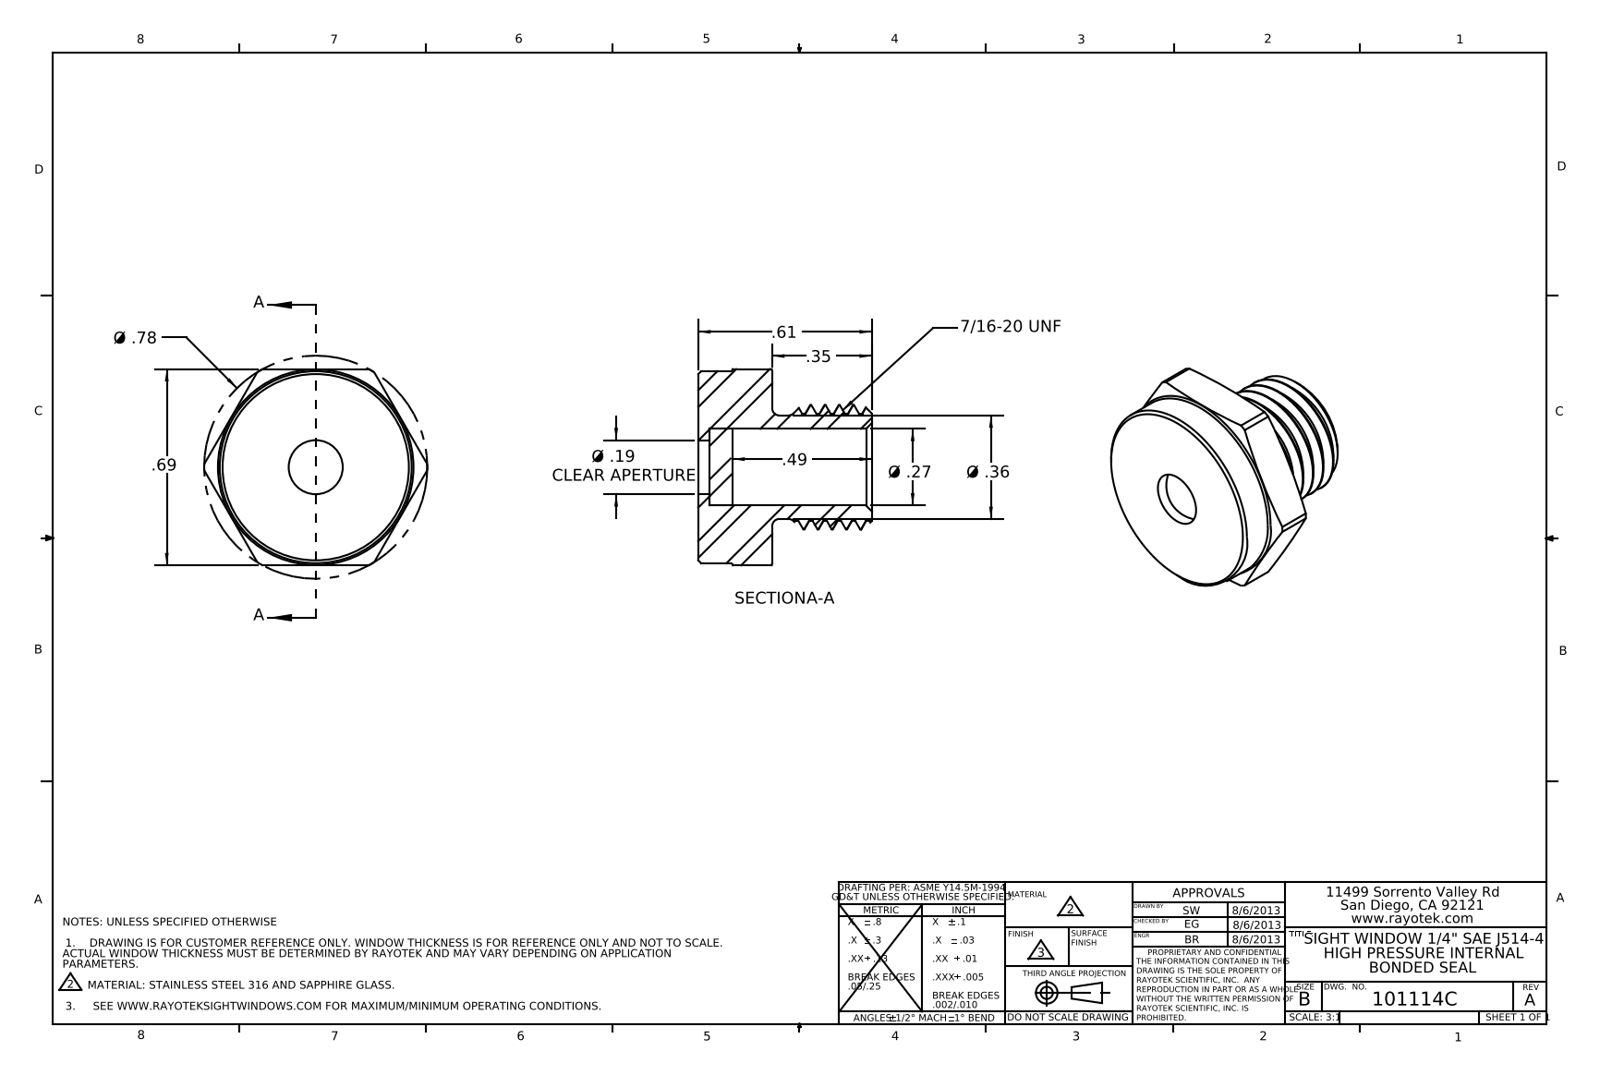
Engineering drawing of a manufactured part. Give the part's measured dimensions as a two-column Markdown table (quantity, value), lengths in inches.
| quantity | value |
| --- | --- |
| part name | 403114 |
| STEP written by | SolidWorks 2012 (AUTOMOTIVE_DESIGN) |
| units | inches |
| bodies | 2 solids, 61 faces (12 planar, 26 cylindrical, 23 other) |
| overall size | 0.785 × 0.69 × 0.61 |
| volume | 0.113 in³ |
| surface area | 2.652 in² |
| round holes (diameter × count) | 0.19 × 1, 0.27 × 1 |
| round bosses / shafts (diameter × count) | 0.675 × 1, 0.437 × 1, 0.364 × 1 |
| partial cylindrical surfaces (radius × count) | 0.392 × 1 |
| main face-to-face distances | 0.26, 0.69, 0.22, 0.04, 0.14, 0.08, 0.12, 0.35, 0.49, 0.57 |
